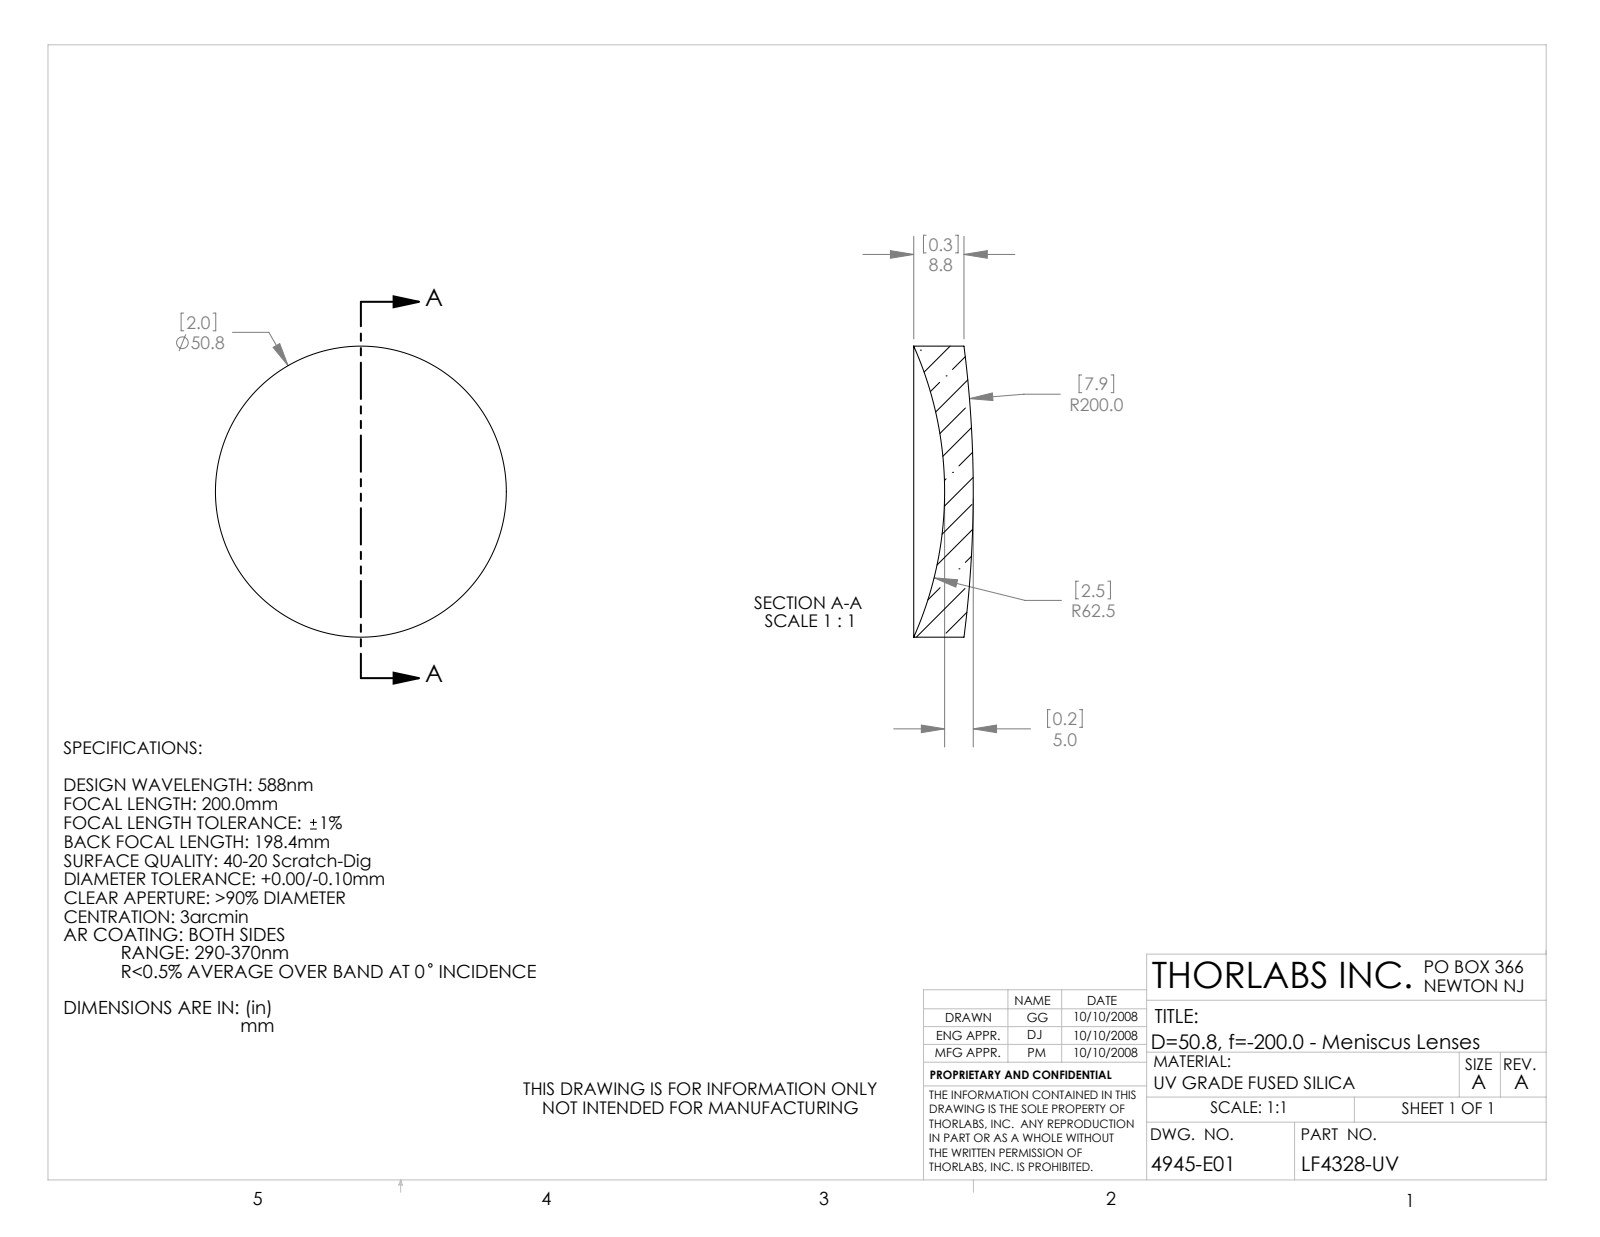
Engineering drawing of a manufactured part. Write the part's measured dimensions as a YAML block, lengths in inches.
part_name: "4945-E0W"
step_written_by: "SolidWorks 2007 (CONFIG_CONTROL_DESIGN)"
units: inches
bodies: {solids: 1, faces: 6, planar: 0, cylindrical: 2, other: 4}
overall_size: [2, 2, 0.409]
volume: 0.847
surface_area: 8.609
round_bosses_or_shafts:
  - {diameter: 2, count: 1}
